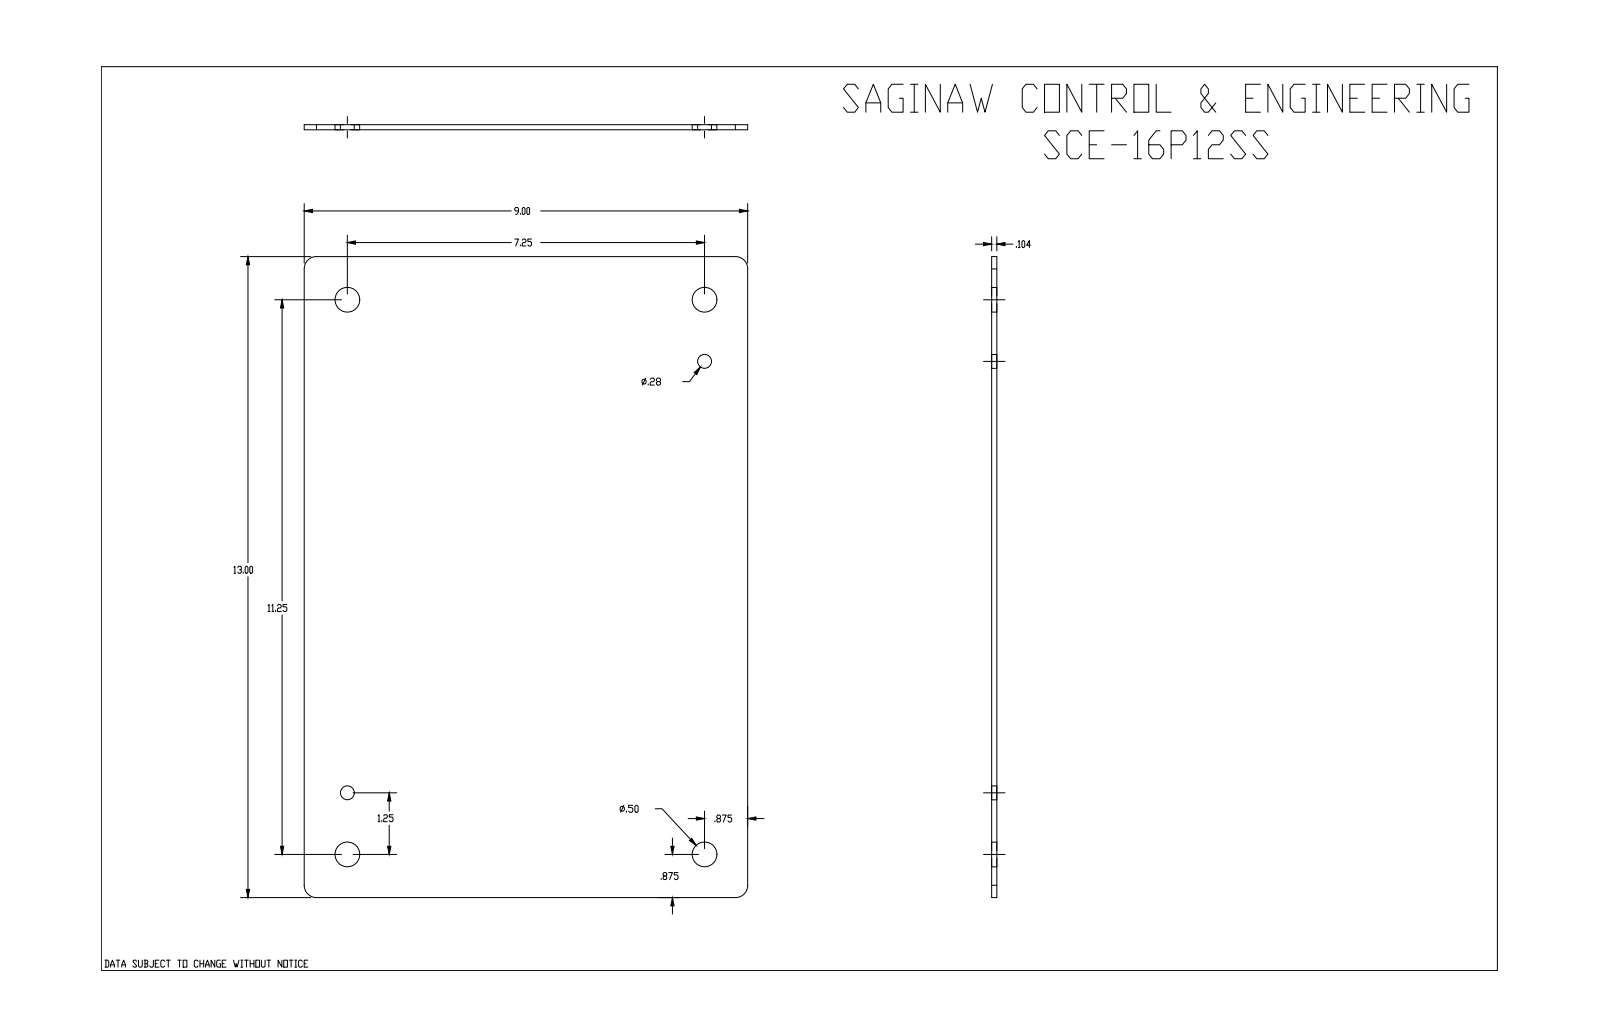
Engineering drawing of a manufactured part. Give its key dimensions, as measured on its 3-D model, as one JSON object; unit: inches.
{"part_name": "SCE-16P12SS", "step_written_by": "SolidWorks 2019 (CONFIG_CONTROL_DESIGN)", "units": "inches", "bodies": {"solids": 1, "faces": 16, "planar": 6, "cylindrical": 10, "other": 0}, "overall_size": [13, 9, 0.104], "volume_in3": 12.07, "surface_area_in2": 237.4, "round_holes": [[0.5, 4], [0.281, 2]], "partial_cylinders_radius": [[0.25, 4]], "face_to_face_distances": [0.104, 9, 13], "hole_center_spacings": [1.25, 7.25, 7.357, 10, 11.25, 12.352, 13.384, 11.363]}
